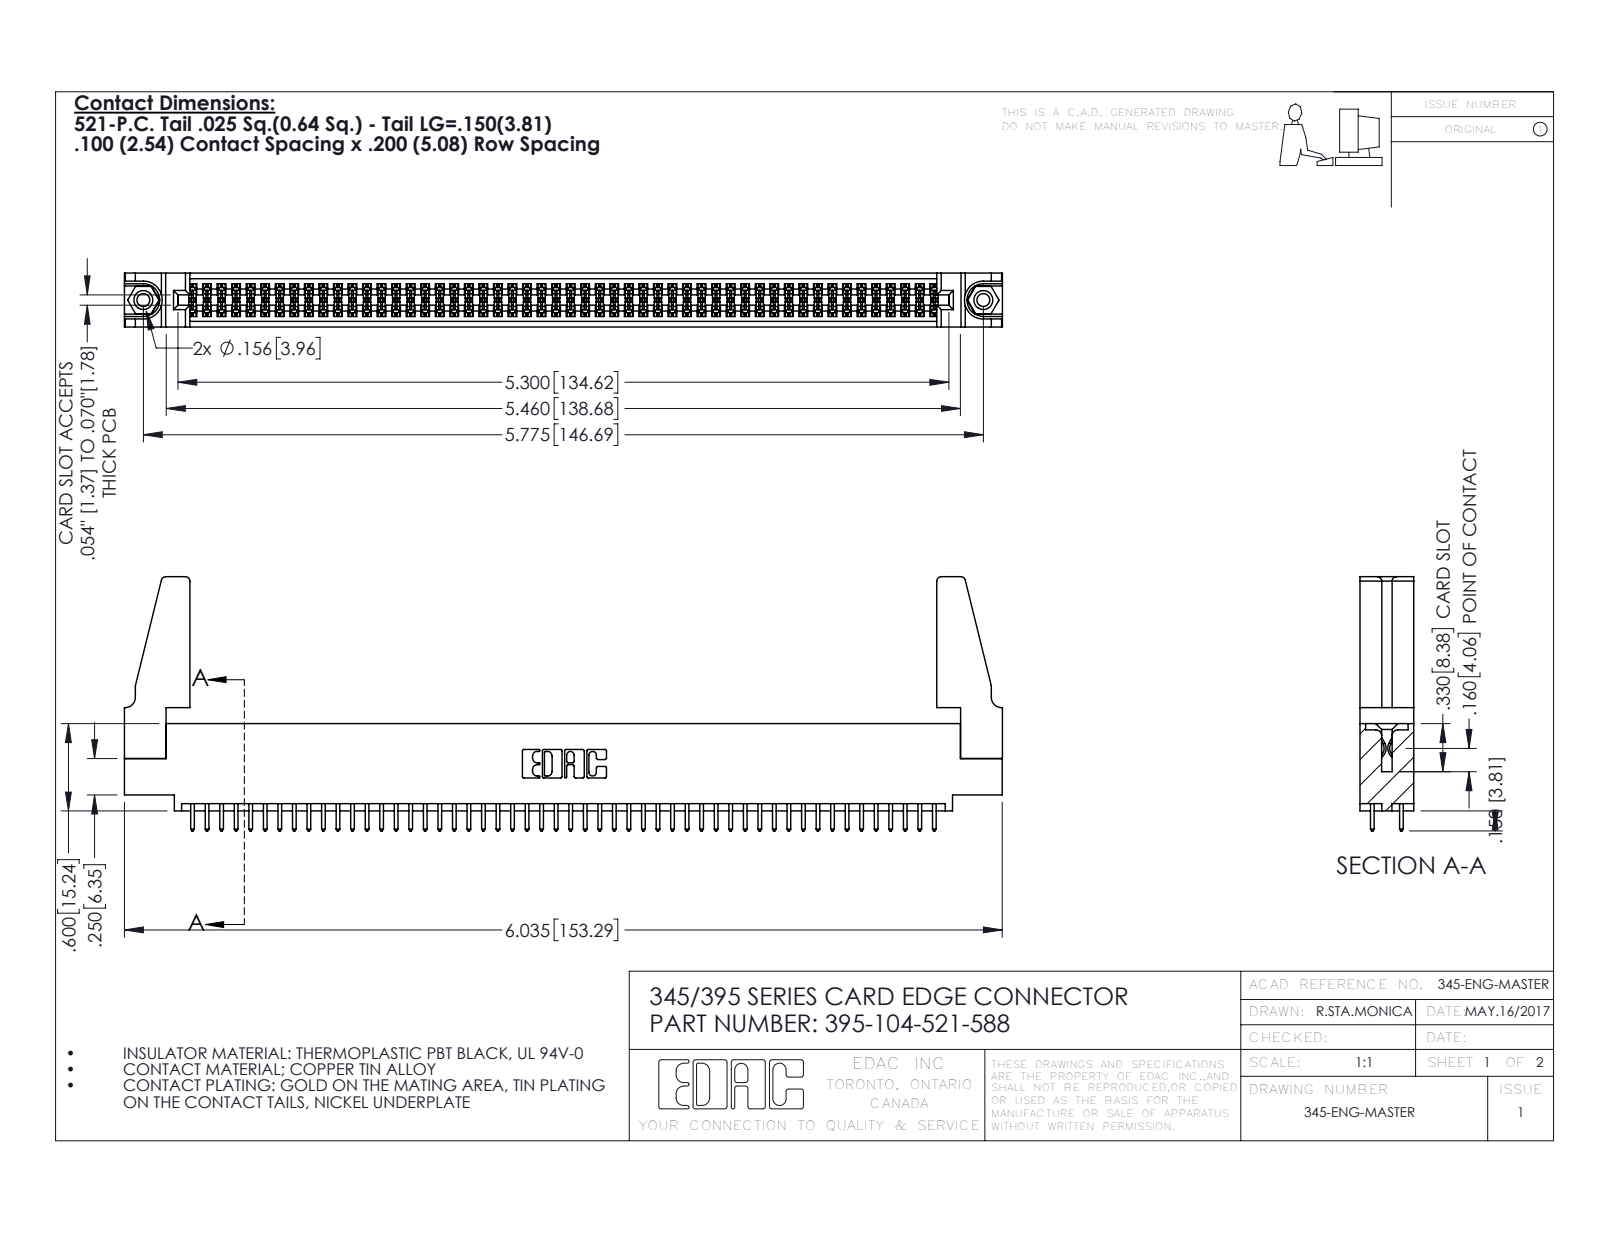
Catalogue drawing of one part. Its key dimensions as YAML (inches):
part_name: "345-250-001_345-250-001-102; 395-104-521-588; 345-220-078_345-220-088; 345-292-001_345-293-121 (+1 more)"
step_written_by: "SolidWorks 2016 (CONFIG_CONTROL_DESIGN)"
units: inches
bodies: {solids: 109, faces: 5454, planar: 3588, cylindrical: 1850, other: 16}
overall_size: [6.036, 1.747, 0.37]
volume: 1.106
surface_area: 38.93
round_holes:
  - {diameter: 0.089, count: 2}
  - {diameter: 0.125, count: 2}
  - {diameter: 0.156, count: 2}
  - {diameter: 0.064, count: 1}
round_bosses_or_shafts:
  - {diameter: 0.155, count: 2}
partial_cylinders:
  - {radius: 0.006, count: 156}
  - {radius: 0.01, count: 104}
  - {radius: 0.01, count: 22}
  - {radius: 0.03, count: 8}
  - {radius: 0.007, count: 6}
  - {radius: 0.031, count: 6}
  - {radius: 0.026, count: 3}
  - {radius: 0.014, count: 2}
face_to_face_distances: [0.072, 0.298, 0.37, 0.2, 0.098, 0.272, 0.025, 0.225, 0.175, 0.149]
hole_center_spacings: [0.27, 5.539, 5.775]
